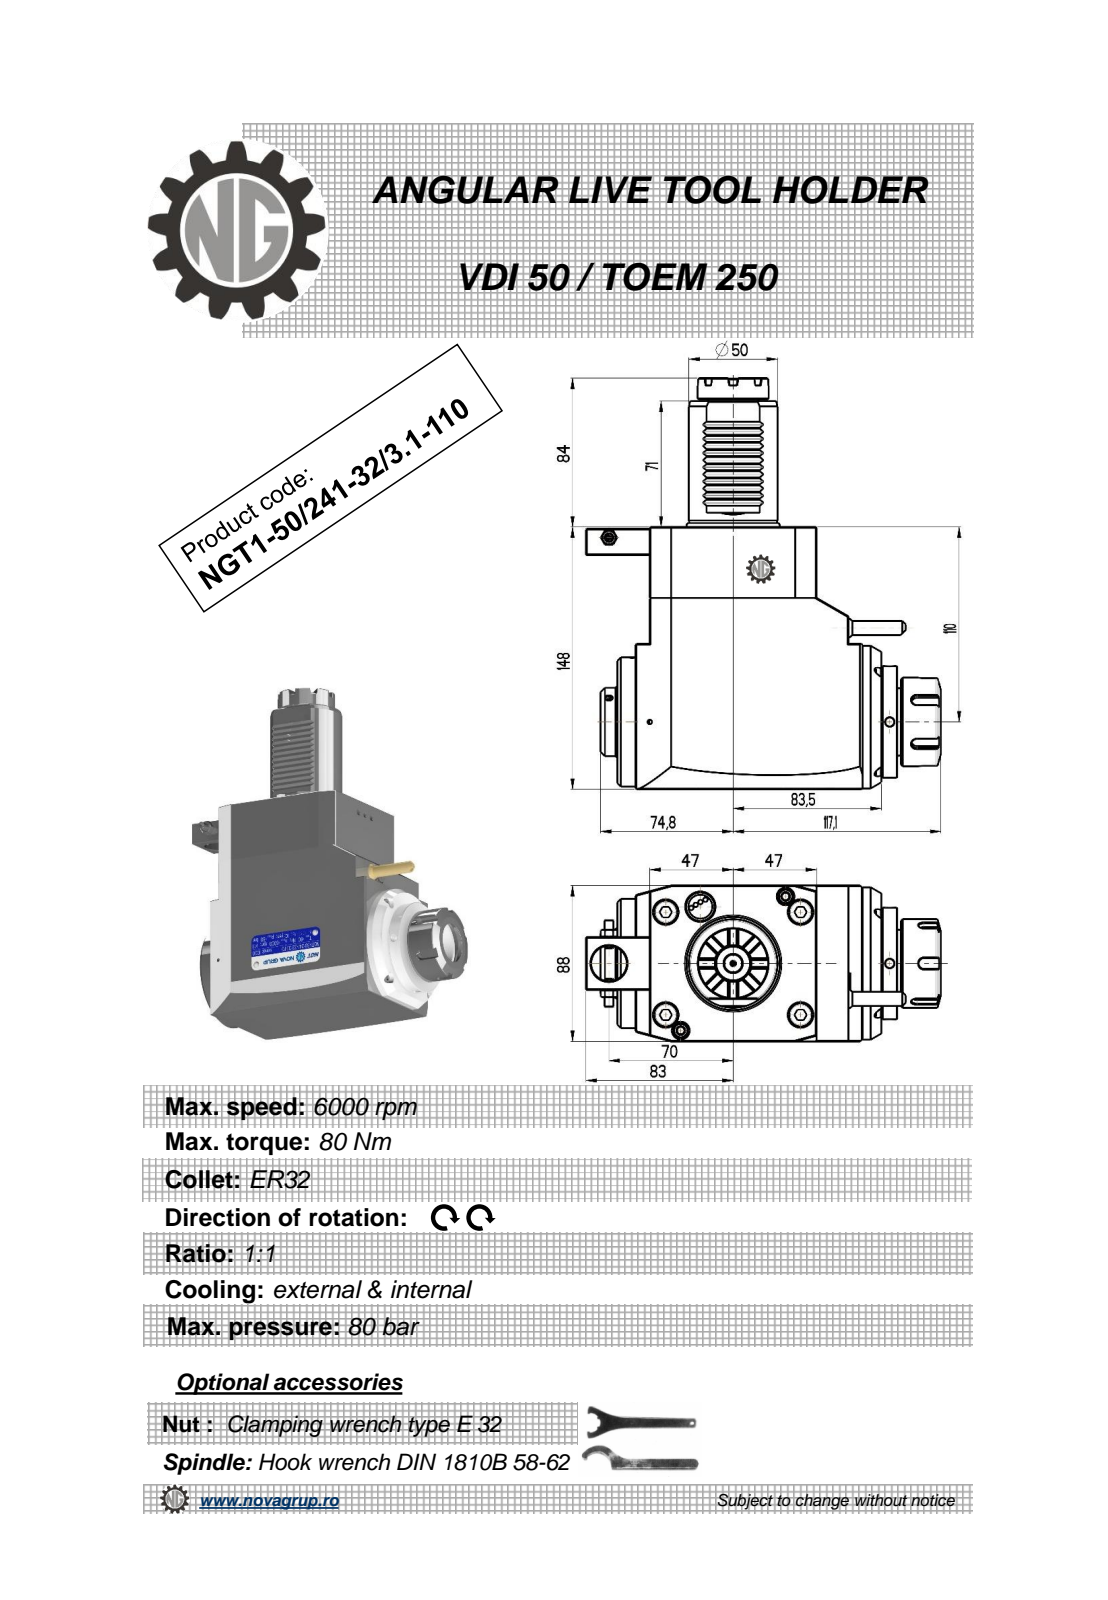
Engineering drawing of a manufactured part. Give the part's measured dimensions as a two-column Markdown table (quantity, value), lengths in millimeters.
| quantity | value |
| --- | --- |
| part name | NGT1_50_241_32_3_1_110 |
| STEP written by | PRO/ENGINEER BY PARAMETRIC TECHNOLOGY CORPORATION, 2010280 (CONFIG_CONTROL_DESIGN) |
| units | millimeters |
| bodies | 1 solid, 482 faces (233 planar, 90 cylindrical, 159 other) |
| overall size | 232 × 200.1 × 88 |
| volume | 1 824 000 mm³ |
| surface area | 115 094 mm² |
| round holes (diameter × count) | 5 × 3, 3 × 1, 9.5 × 1, 20 × 1, 27 × 1 |
| round bosses / shafts (diameter × count) | 50 × 2, 40 × 2, 86 × 1, 73 × 1, 63 × 1, 50.5 × 1, 41 × 1, 38.5 × 1 |
| partial cylindrical surfaces (radius × count) | 0.26 × 12, 0.3 × 12, 0.2 × 6, 3 × 5 |
| main face-to-face distances | 88, 148, 8, 94, 130.5, 36.5, 120, 18.3, 112.3, 148.8 |
| hole center spacings | 52.46, 56.65, 101.5, 158.25 |
